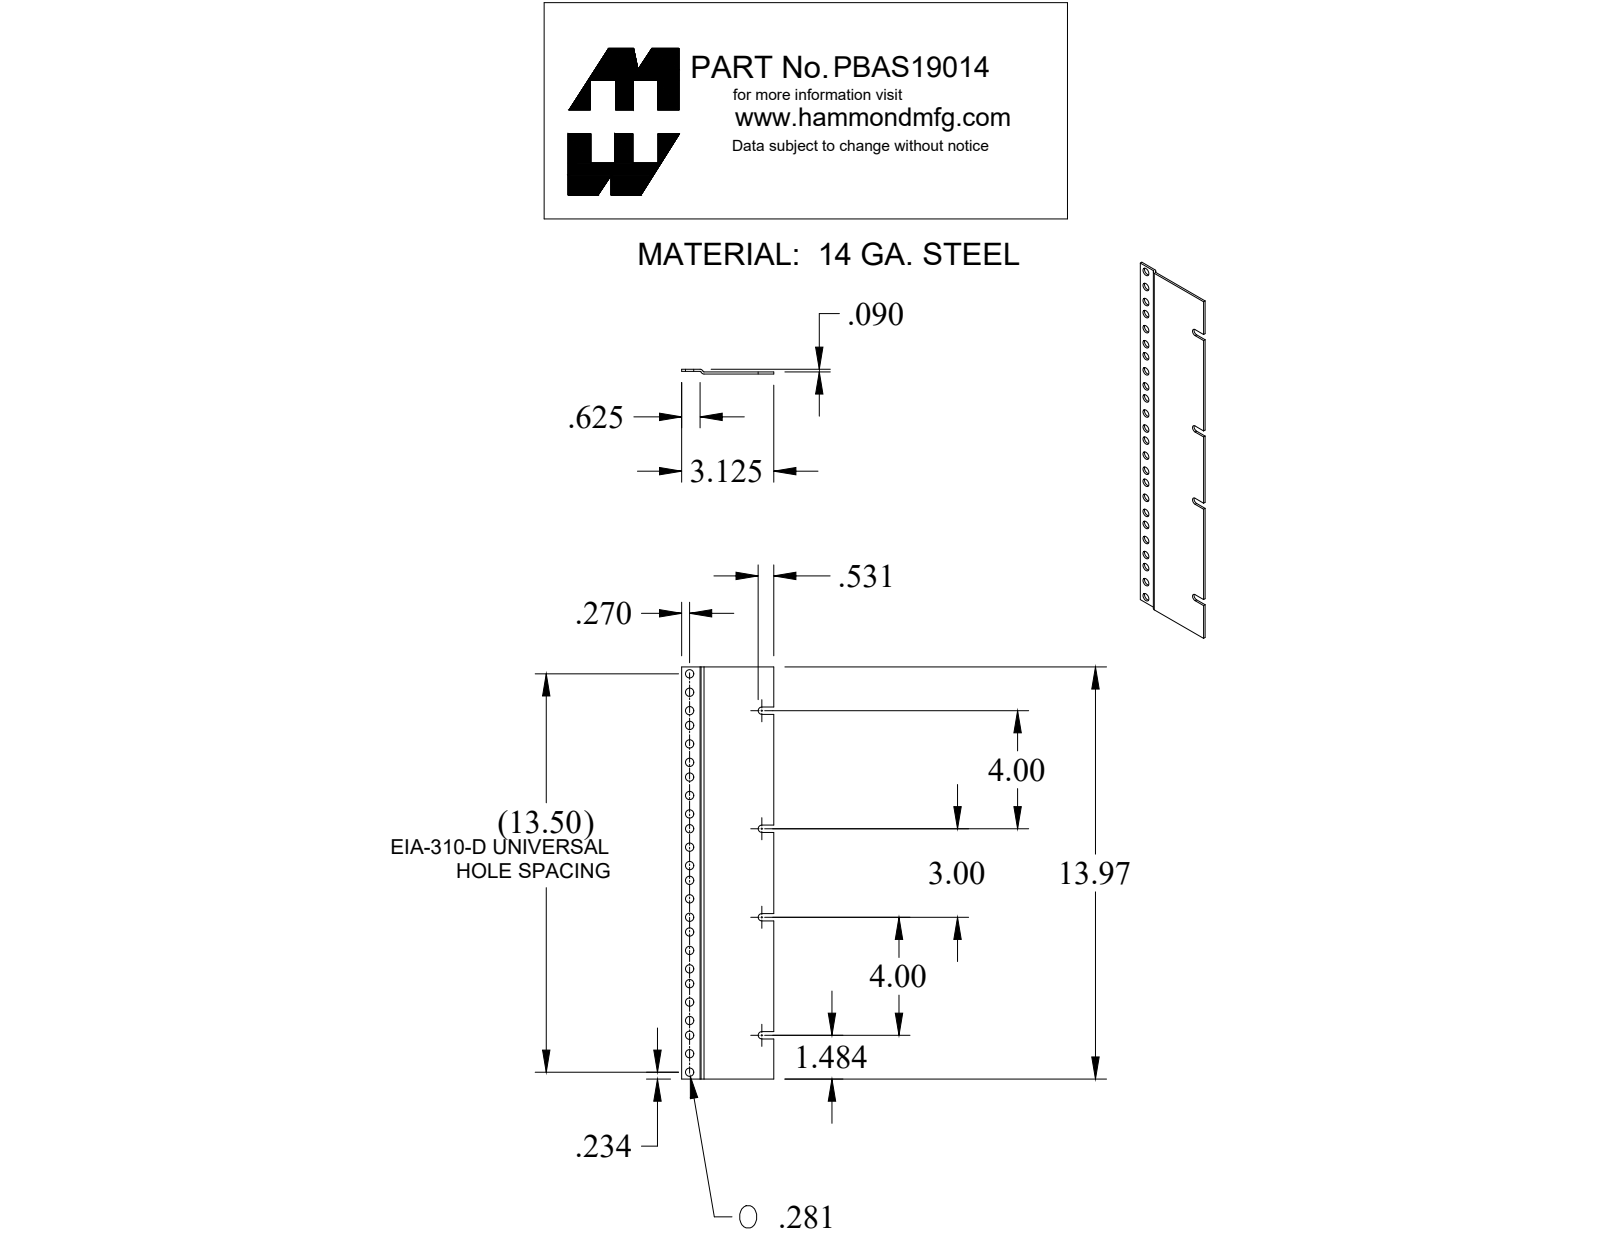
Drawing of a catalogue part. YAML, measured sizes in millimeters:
part_name: "PBAS19014BK2"
step_written_by: "SolidWorks 2019 (CONFIG_CONTROL_DESIGN)"
units: millimeters
bodies: {solids: 1, faces: 52, planar: 20, cylindrical: 32, other: 0}
overall_size: [354.8, 79.4, 4.1]
volume: 49770
surface_area: 57180
round_holes:
  - {diameter: 7.1, count: 24}
partial_cylinders:
  - {radius: 3.2, count: 4}
  - {radius: 0.9, count: 2}
  - {radius: 2.7, count: 2}
face_to_face_distances: [1.8, 2.3, 4.1, 0.5, 2.3, 1.8, 79.4, 354.8, 101.6, 6.4]
hole_center_spacings: [44.5, 88.9, 133.4, 15.9, 15.9, 28.6, 31.8, 60.3]
